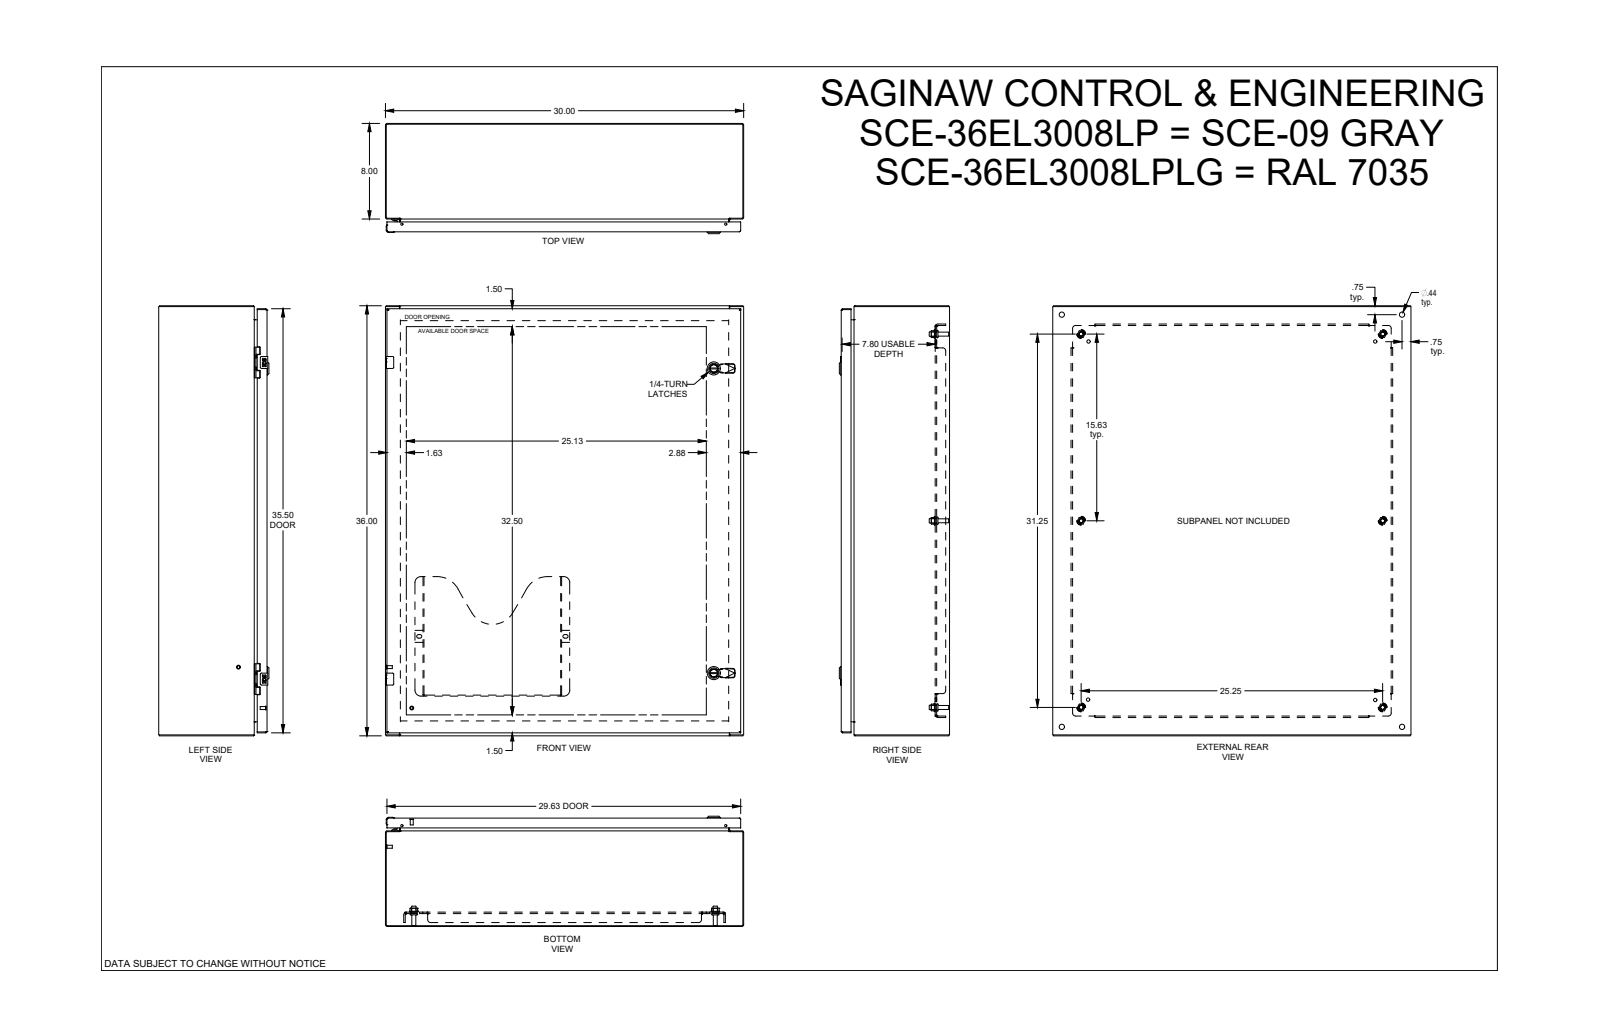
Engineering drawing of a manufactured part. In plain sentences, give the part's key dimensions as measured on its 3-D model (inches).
The part is named "SCE-36EL3008LP". Its 3-D file was written by "SolidWorks 2021 (AUTOMOTIVE_DESIGN)". It is 51 solids with 2989 faces: 1139 planar, 888 cylindrical and 962 other. Overall it measures 36 by 30 by 9.23 inches. Its volume is 407.5 cubic inches and its surface area 9 594 square inches. Round holes: 6 of diameter 0.367, 6 of diameter 0.5, 4 of diameter 0.172, 4 of diameter 0.205, 4 of diameter 0.244, 4 of diameter 0.266, 4 of diameter 0.281, 4 of diameter 0.375, 4 of diameter 0.437, 2 of diameter 0.04, 2 of diameter 0.188, 2 of diameter 0.197. Round bosses or shafts: 6 of diameter 0.366, 6 of diameter 0.332, 6 of diameter 0.17, 4 of diameter 0.25, 4 of diameter 0.248, 4 of diameter 0.24, 3 of diameter 0.196, 2 of diameter 1.102. Partial cylindrical surfaces (rounded edges, fillets, slot ends): 56 of radius 0.012, 40 of radius 0.01, 20 of radius 0.015, 20 of radius 0.02, 17 of radius 0.04, 13 of radius 0.06, 12 of radius 0.029, 12 of radius 0.1. The main face-to-face distances are 0.075, 0.06, 9.073, 8.998, 9.013, 8.938, 1.2, 7.873, 1, 0.125. The hole center spacings are 0.985, 15.625, 26.5, 32.915, 42.462, 30.638, 31.25, 0.02.
